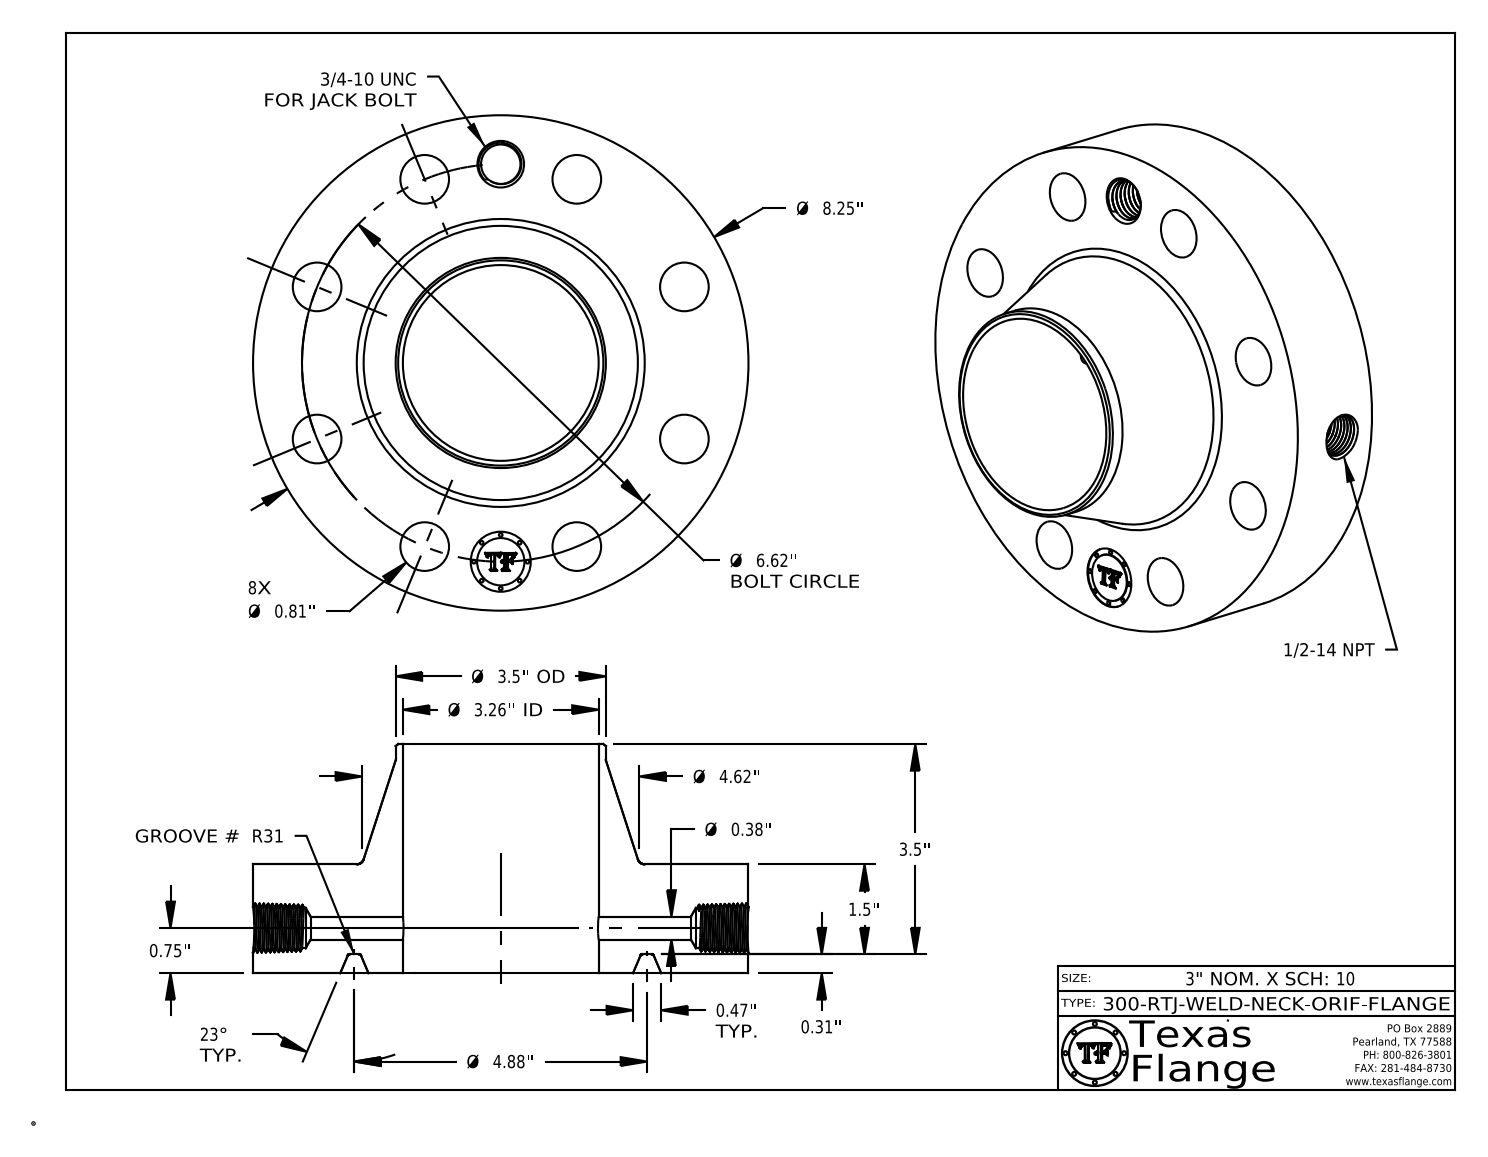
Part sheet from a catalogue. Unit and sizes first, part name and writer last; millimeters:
Units: millimetres
Overall size (bounding box): 209.6 × 209.6 × 96.9
Round holes (diameter × count): ⌀20.6 ×8, ⌀9.7 ×1, ⌀16.7 ×1, ⌀17.1 ×1, ⌀25.4 ×1, ⌀82.8 ×1
Round bosses / shafts (diameter × count): ⌀1.5 ×8, ⌀209.6 ×1, ⌀88.9 ×1, ⌀20 ×1
Main face-to-face distances: 46.1, 8, 38.1, 96.9, 88.9, 50.8, 0.4, 45.7, 37.7, 51.2
Hole centre spacings: 84.1, 118.9, 155.3, 168.1, 32.8, 64.3, 64.3, 93.4
Volume: 1 300 000 mm³ · Surface area: 157 900 mm²
Bodies: 1 solid, 795 faces (370 planar, 96 cylindrical, 329 other)
Part name (STEP PRODUCT): 300-RTJ-WELD-NECK
STEP written by: CATIA V5 STEP AP214 (AUTOMOTIVE_DESIGN)
